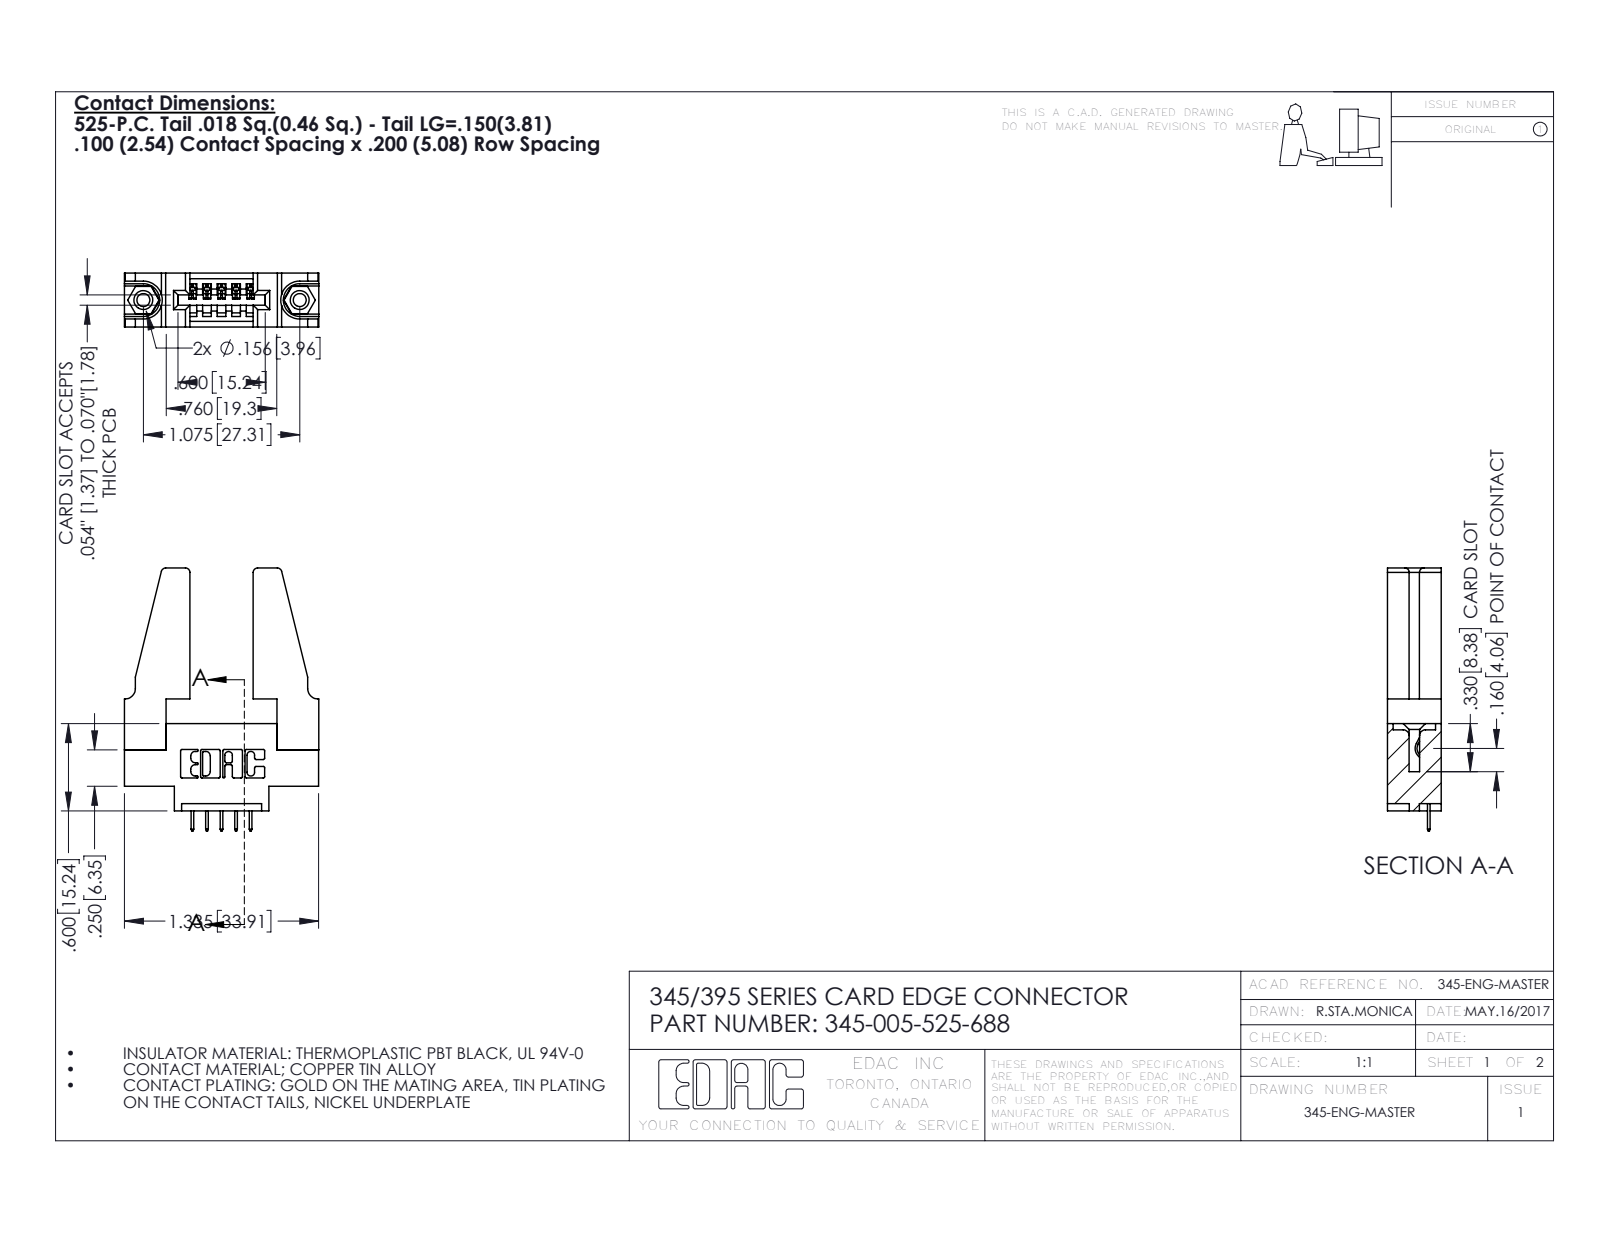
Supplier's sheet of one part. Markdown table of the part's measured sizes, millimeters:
| quantity | value |
| --- | --- |
| part name | 345 Part_0.170 Offset - 0.156 Dia-TH; 345-292-001_345-293-125; 345-220-078_345-220-088; 345-250-001_345-250-001-102 (+1 more) |
| STEP written by | SolidWorks 2020 (CONFIG_CONTROL_DESIGN) |
| units | millimeters |
| bodies | 10 solids, 564 faces (386 planar, 162 cylindrical, 16 other) |
| overall size | 45.9 × 33.9 × 9.4 |
| volume | 6 050 mm³ |
| surface area | 6 388 mm² |
| round holes (diameter × count) | 2.3 × 2, 3.2 × 2, 4 × 2, 1.6 × 1 |
| round bosses / shafts (diameter × count) | 3.9 × 2 |
| partial cylindrical surfaces (radius × count) | 0.3 × 22, 0.2 × 10, 0.8 × 8, 0.2 × 6, 0.8 × 6, 0.7 × 3, 0.8 × 2, 1 × 2 |
| main face-to-face distances | 9.4, 1.8, 7.6, 5.1, 3.8, 3.8, 5.6, 2, 11, 7.3 |
| hole center spacings | 6.9, 21.5, 27.3 |
